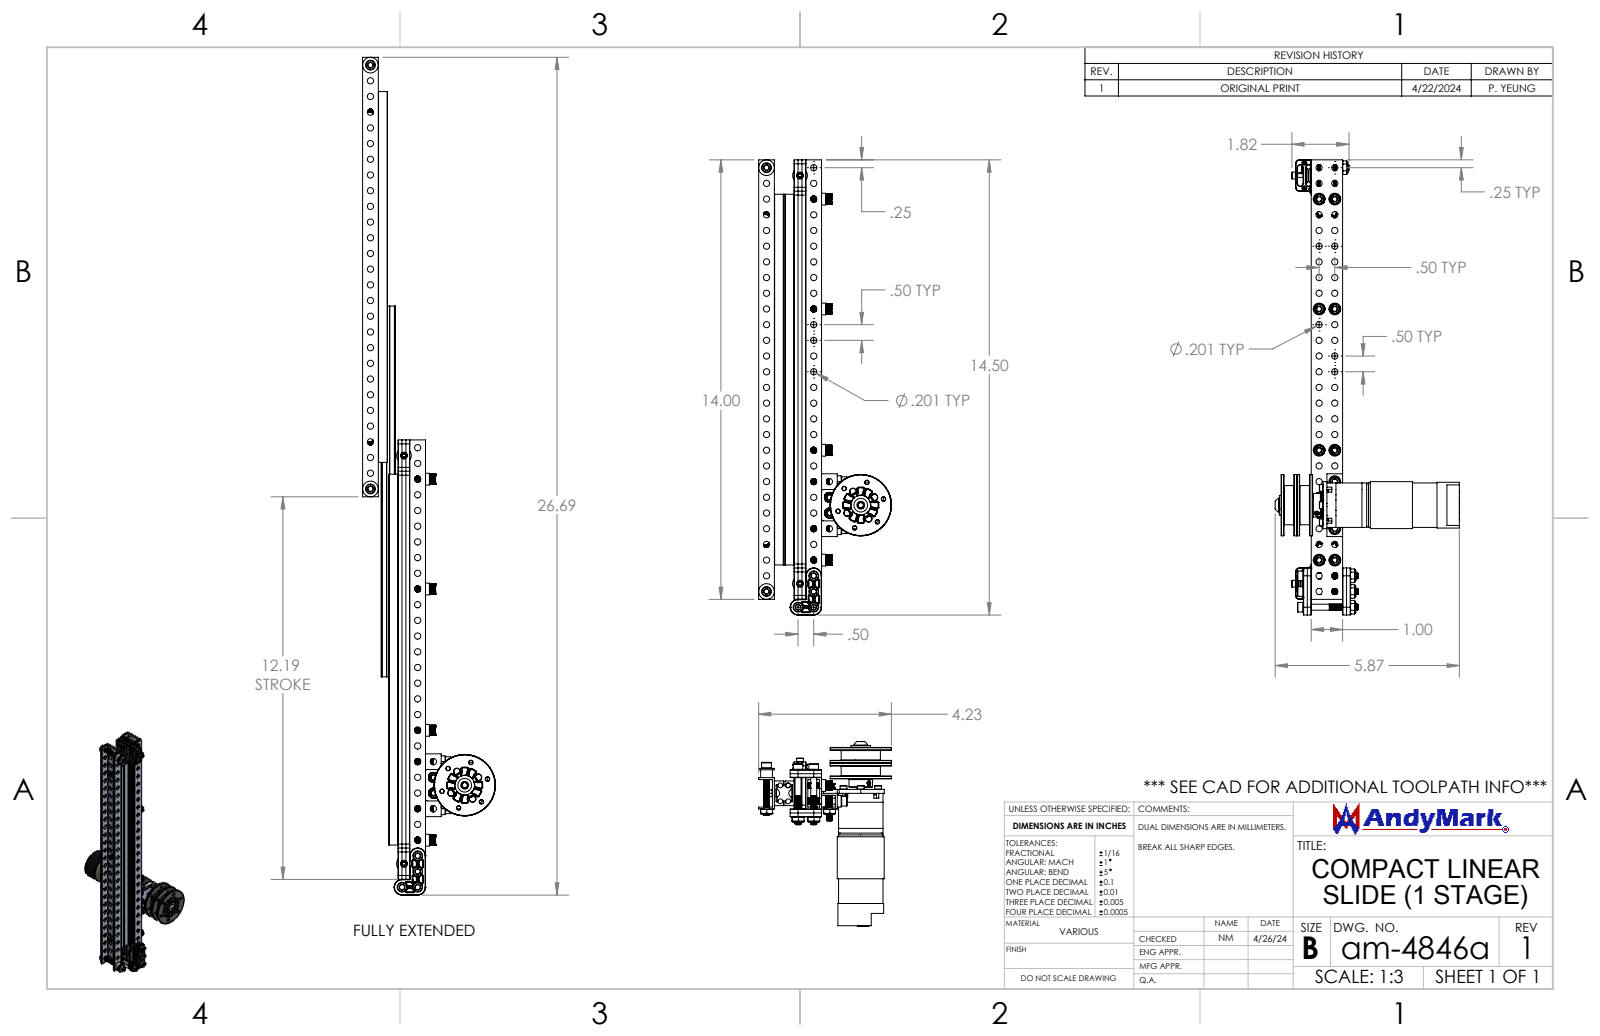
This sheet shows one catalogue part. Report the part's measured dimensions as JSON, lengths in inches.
{"part_name": "SAR330_111; am-5036 Robits Spool 375 Hex Large_Bolt Circle; 7804K117_STAINLESS STEEL BALL BEARING_7804K117; am-1027 (+8 more)", "step_written_by": "SolidWorks 2024 (AUTOMOTIVE_DESIGN)", "units": "inches", "bodies": {"solids": 158, "faces": 19843, "planar": 3856, "cylindrical": 6946, "other": 9041}, "overall_size": [14.5, 5.875, 4.231], "volume_in3": 20.52, "surface_area_in2": 443.1, "round_holes": [[0.201, 122], [0.164, 72], [0.161, 18], [0.239, 18], [0.125, 16], [0.125, 13], [0.098, 10], [0.194, 10], [0.138, 3], [0.315, 3], [0.041, 2], [0.126, 2]], "round_bosses_or_shafts": [[0.19, 19], [0.118, 13], [0.375, 12], [0.313, 10], [0.217, 10], [0.312, 8], [0.093, 8], [0.236, 4]], "partial_cylinders_radius": [[0.01, 1452], [0.008, 40], [0.064, 34], [0.031, 32], [0.082, 18], [0.125, 10], [0.075, 8], [0.089, 8]], "face_to_face_distances": [0.063, 0.5, 0.437, 0.063, 1, 1.005, 0.375, 1.505, 0.63, 0.875], "hole_center_spacings": [0.5, 1, 1.5, 2, 2.5, 3, 3.5, 4]}
